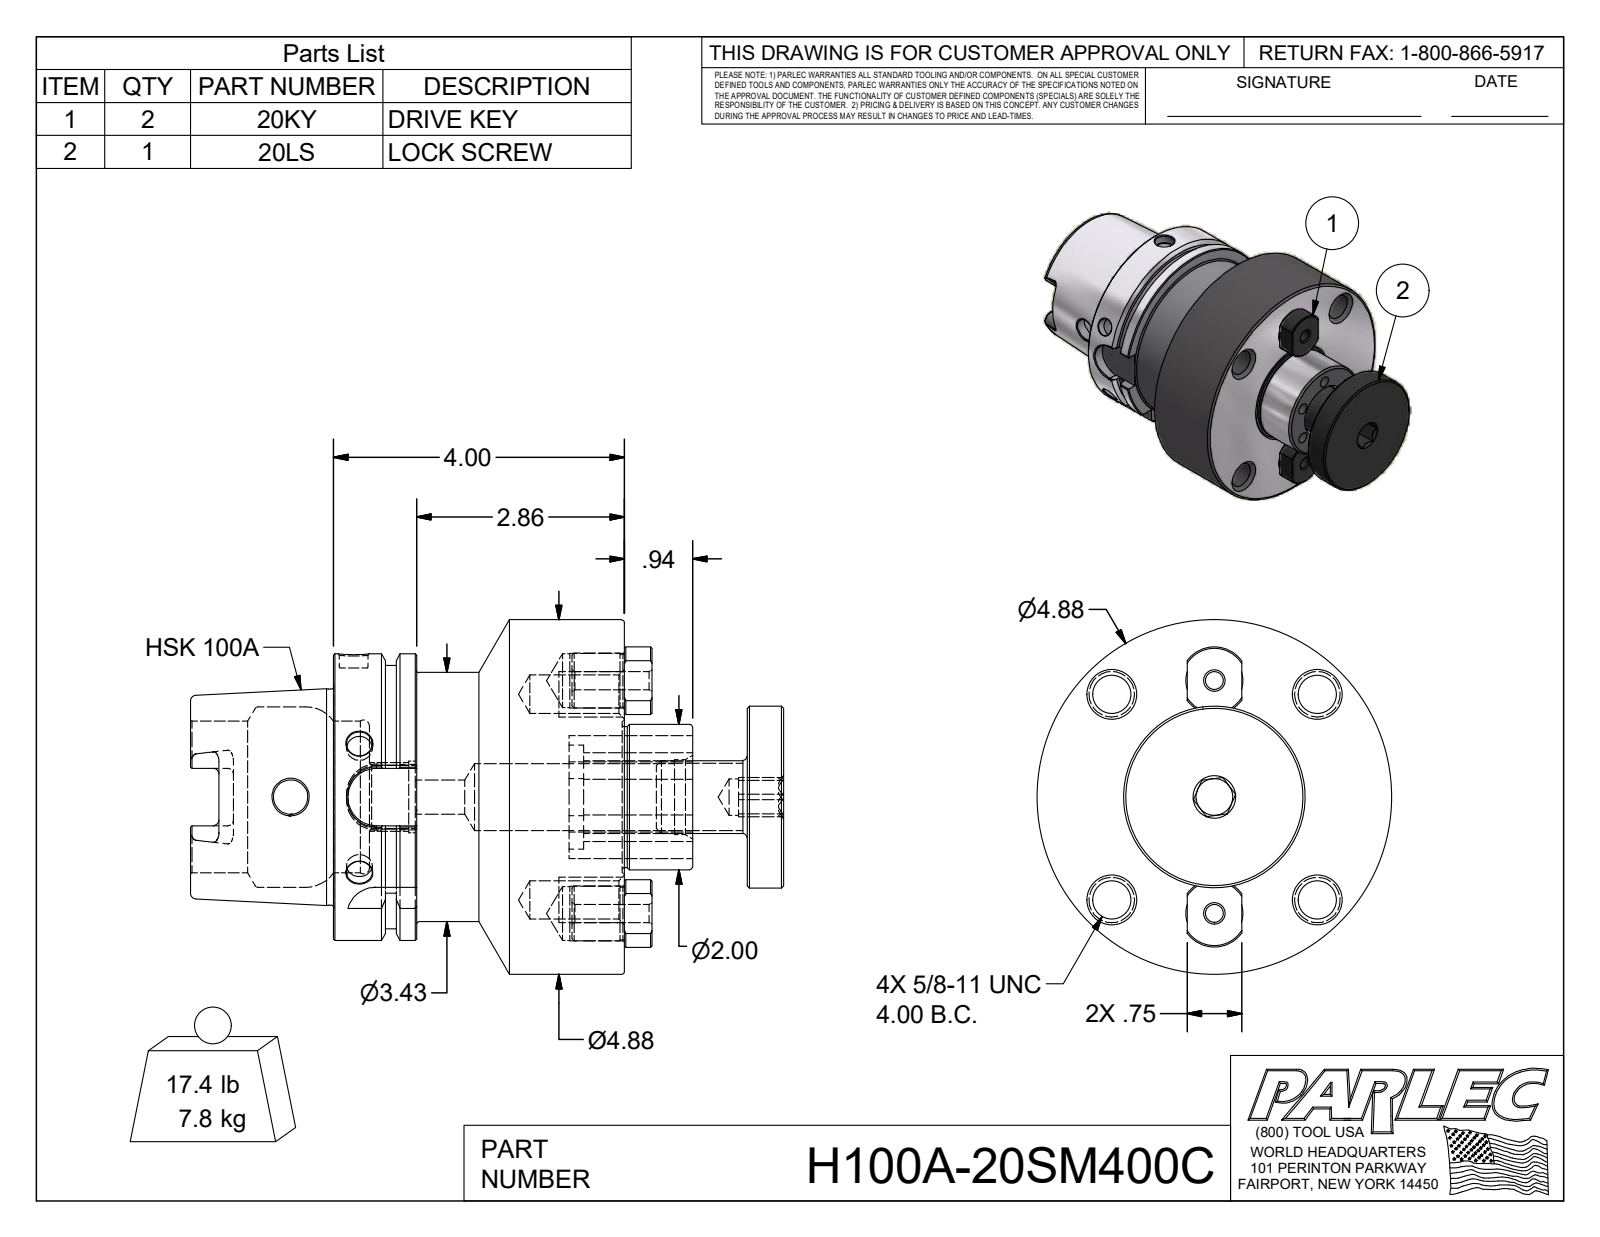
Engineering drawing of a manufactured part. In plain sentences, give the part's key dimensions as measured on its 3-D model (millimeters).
The part is named "H100A-20SM400C; 20KY; 20LS". Its 3-D file was written by "Autodesk Inventor 2018 (AUTOMOTIVE_DESIGN)". It is 4 solids with 240 faces: 76 planar, 75 cylindrical and 89 other. Overall it measures 207.2 by 123.8 by 123.8 millimeters. Its volume is 998 500 cubic millimeters and its surface area 126 500 square millimeters. Round holes: 6 of diameter 6, 4 of diameter 13.4, 2 of diameter 6.4, 2 of diameter 9, 2 of diameter 12, 2 of diameter 18.9, 2 of diameter 19.1, 1 of diameter 10, 1 of diameter 12.8, 1 of diameter 22.4, 1 of diameter 23.4, 1 of diameter 25. Round bosses or shafts: 2 of diameter 19.2, 2 of diameter 18.3, 1 of diameter 123.8, 1 of diameter 100, 1 of diameter 92, 1 of diameter 87, 1 of diameter 75.4, 1 of diameter 63.5. Partial cylindrical surfaces (rounded edges, fillets, slot ends): 6 of radius 2, 4 of radius 4.9, 4 of radius 10, 2 of radius 11.8, 1 of radius 18.4. The main face-to-face distances are 55.5, 101.6, 157.1, 12.7, 144.4, 42.8, 12.5, 31.8, 89.1, 132. The hole center spacings are 18.5, 32, 33.3, 35.2, 36.2, 39.9, 49.4, 50.8.
